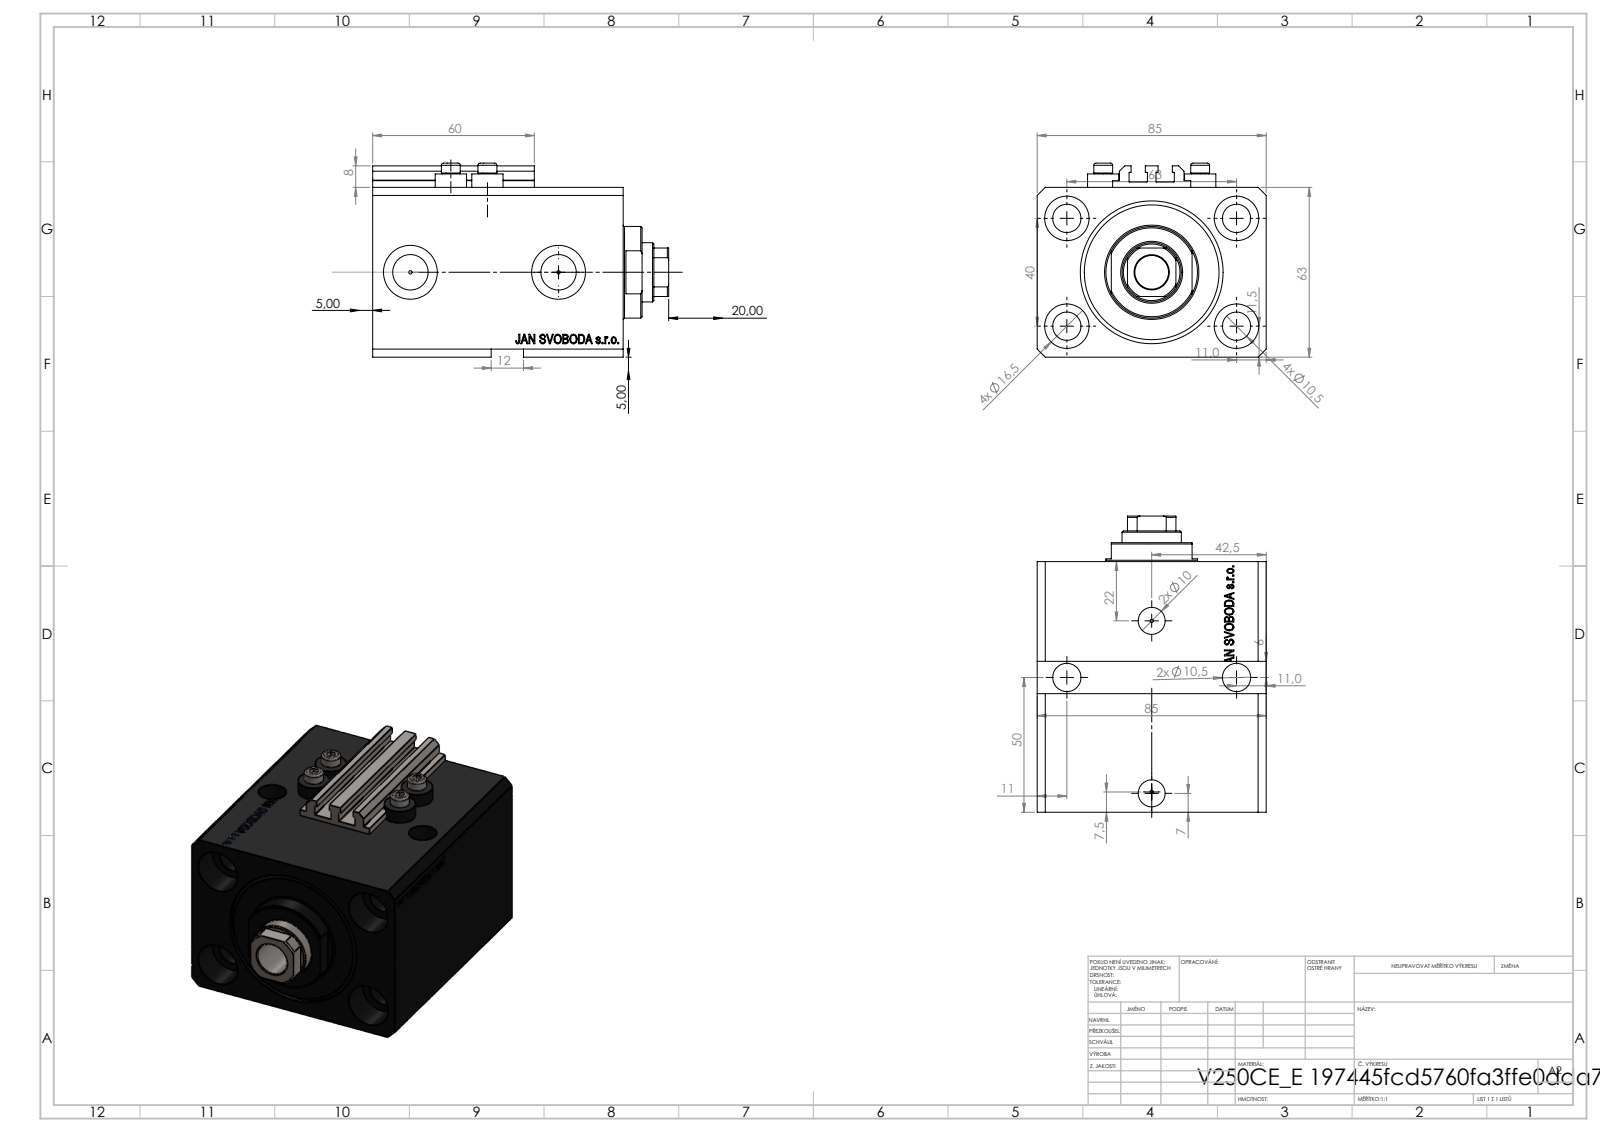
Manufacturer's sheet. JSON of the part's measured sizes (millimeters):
{"part_name": "V250CE_E_Body; V250CE_C_VCP; ALLEN BOLT V250CE; V250CE_VC_E", "step_written_by": "SolidWorks 2019 (CONFIG_CONTROL_DESIGN)", "units": "millimeters", "bodies": {"solids": 8, "faces": 1087, "planar": 535, "cylindrical": 126, "other": 426}, "overall_size": [110, 85, 72], "volume_mm3": 437253, "surface_area_mm2": 95786, "round_holes": [[10.5, 6], [1.25, 4], [4, 4], [16.5, 4], [10, 2], [13.16, 2], [20, 2], [12.5, 1], [22, 1], [40, 1], [53, 1]], "round_bosses_or_shafts": [[11.6, 4], [7, 4], [34, 1]], "partial_cylinders_radius": [[0.2, 10], [10.5, 1]], "face_to_face_distances": [63, 85, 93, 17, 76, 11.4, 64.6, 81.6, 3, 65], "hole_center_spacings": [37.31, 63, 13.6, 15.4, 24.96, 28.02, 28.43, 33.62]}
